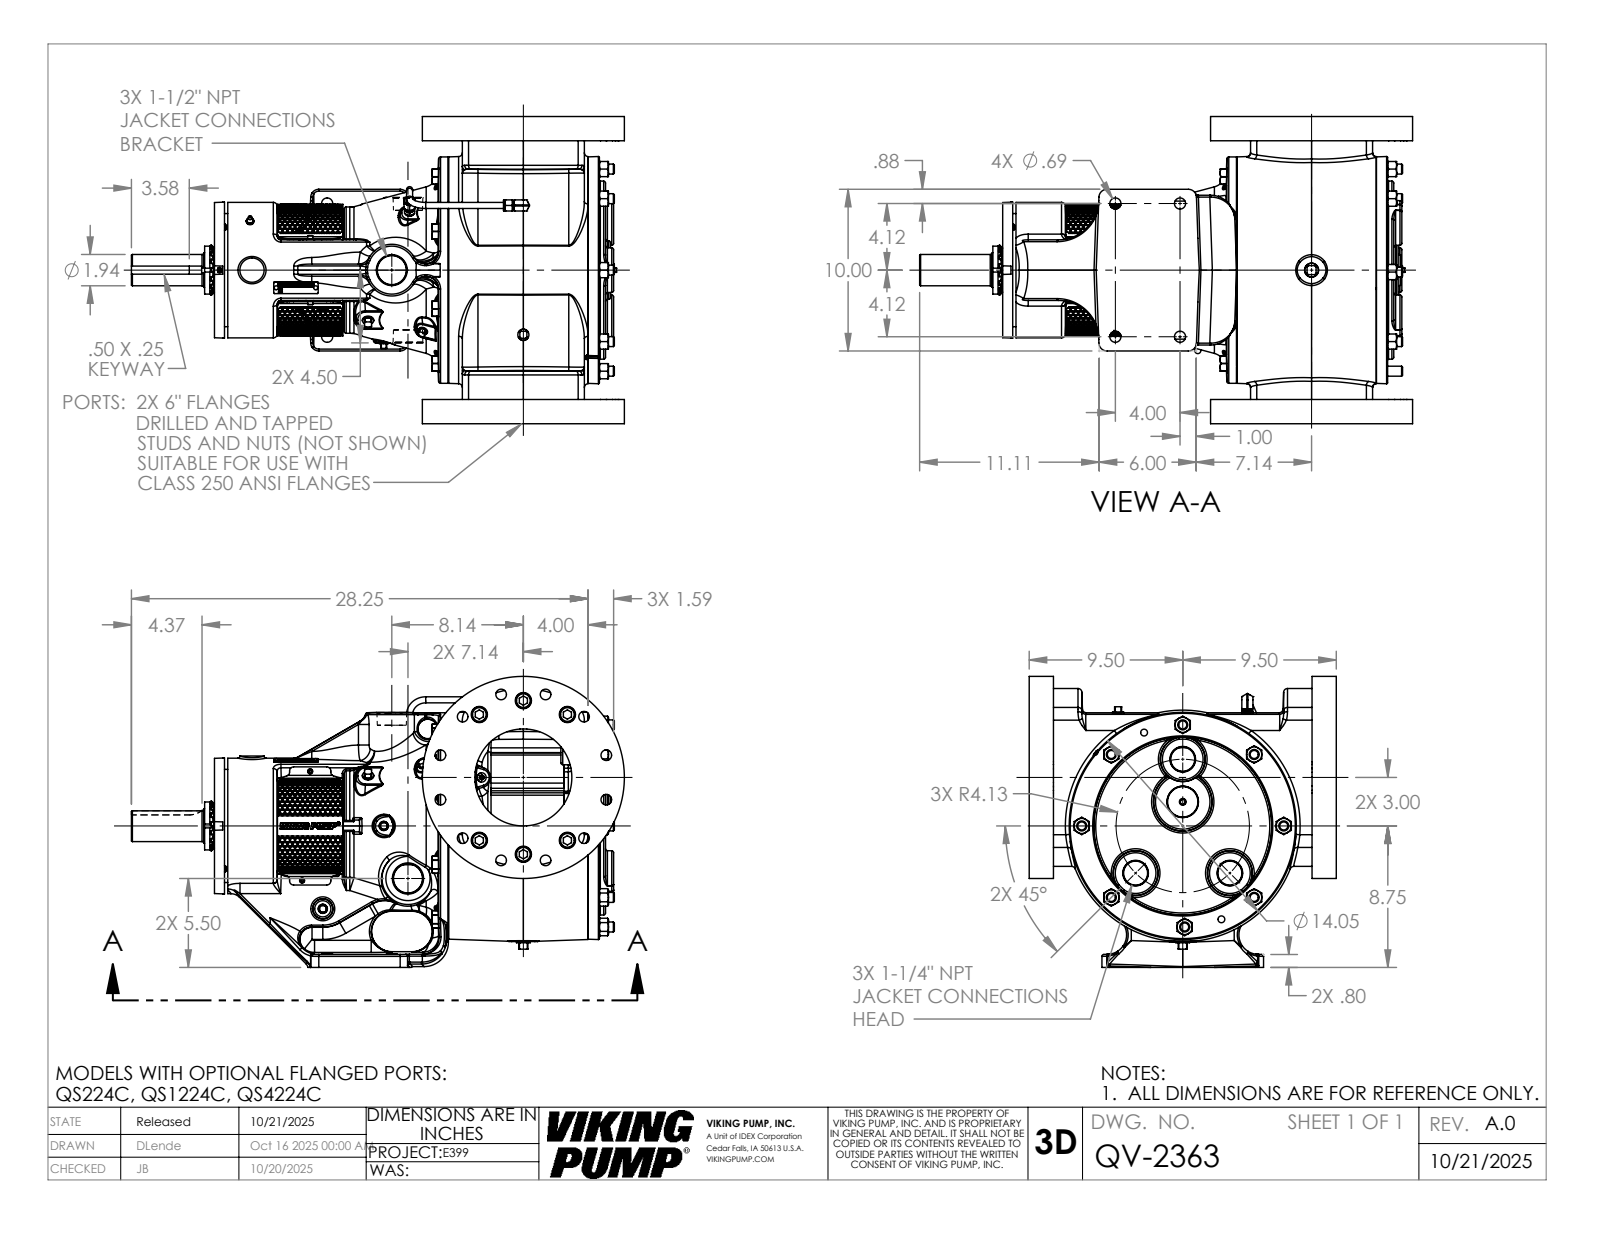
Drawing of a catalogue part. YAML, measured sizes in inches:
part_name: "QV-2363"
step_written_by: "SolidWorks 2024 (AUTOMOTIVE_DESIGN)"
units: inches
bodies: {solids: 1, faces: 3960, planar: 1305, cylindrical: 664, other: 1991}
overall_size: [30.501, 19, 18]
volume: 3019
surface_area: 2532
round_holes:
  - {diameter: 0.656, count: 12}
  - {diameter: 0.25, count: 9}
  - {diameter: 0.266, count: 8}
  - {diameter: 1.157, count: 8}
  - {diameter: 1, count: 6}
  - {diameter: 0.688, count: 4}
  - {diameter: 0.159, count: 2}
  - {diameter: 0.313, count: 2}
  - {diameter: 0.422, count: 2}
  - {diameter: 0.453, count: 1}
  - {diameter: 2.157, count: 1}
  - {diameter: 2.167, count: 1}
round_bosses_or_shafts:
  - {diameter: 0.617, count: 8}
  - {diameter: 0.937, count: 6}
  - {diameter: 0.375, count: 3}
  - {diameter: 0.312, count: 3}
  - {diameter: 0.19, count: 3}
  - {diameter: 0.687, count: 2}
  - {diameter: 0.563, count: 2}
  - {diameter: 0.498, count: 2}
partial_cylinders:
  - {radius: 0.12, count: 54}
  - {radius: 0.75, count: 22}
  - {radius: 0.015, count: 18}
  - {radius: 0.092, count: 18}
  - {radius: 0.07, count: 16}
  - {radius: 0.5, count: 12}
  - {radius: 0.25, count: 10}
  - {radius: 1, count: 10}
face_to_face_distances: [1.5, 17.5, 19, 16, 0.38, 23.817, 24.197, 3.82, 19.998, 20.378]
hole_center_spacings: [5.313, 3.75, 2.079, 10.263, 5.783, 2.713, 2.75, 3.133]
